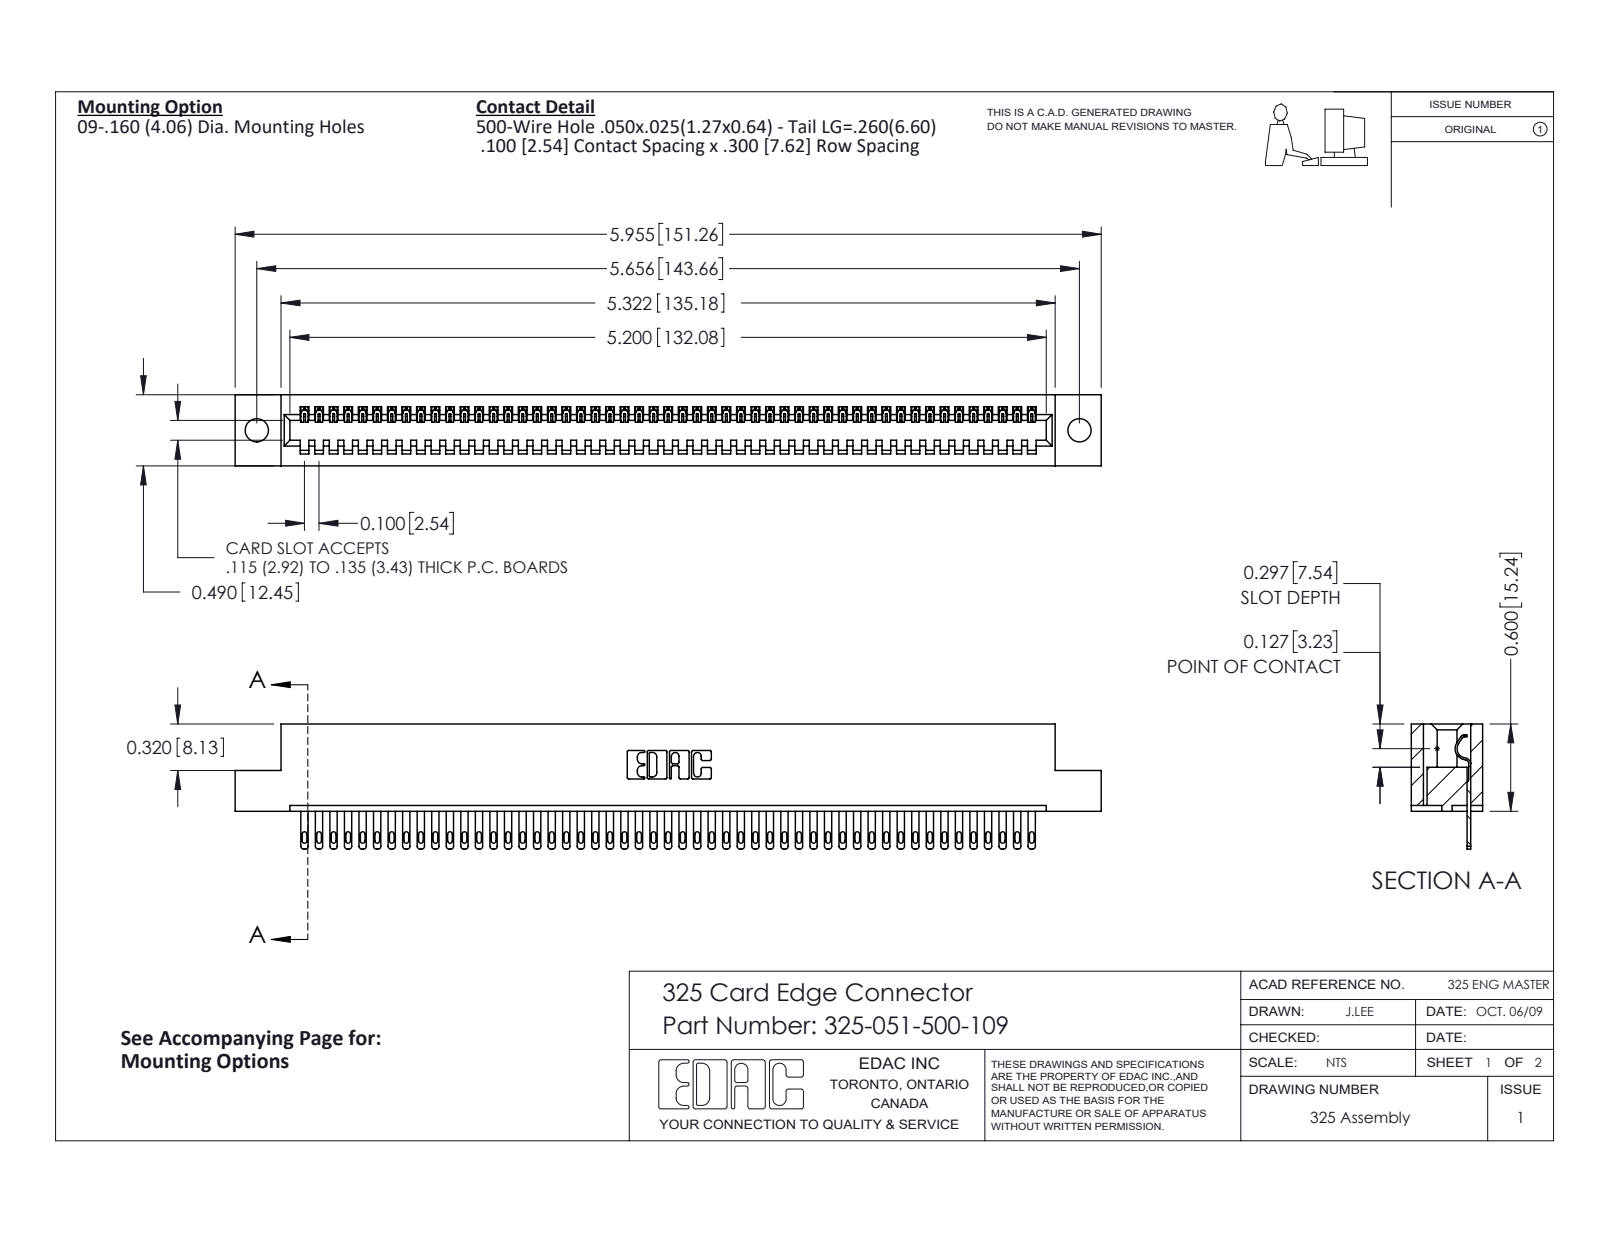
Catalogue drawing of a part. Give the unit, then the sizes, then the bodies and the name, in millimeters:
Units: millimetres
Overall size (bounding box): 151.3 × 21.8 × 12.4
Round holes (diameter × count): ⌀4.1 ×2
Partial cylindrical surfaces — rounded edges, fillets, slot ends (radius × count): R0.2 ×102, R0.4 ×102, R0.5 ×102, R0.3 ×22, R0.2 ×6, R0.8 ×6, R0.7 ×3, R0.4 ×1
Main face-to-face distances: 2.1, 10.3, 12.4, 7.6, 2.7, 9.7, 0.6, 8.3, 14.2, 6.7
Hole centre spacings: 143.7
Volume: 19 070 mm³ · Surface area: 21 010 mm²
Bodies: 52 solids, 2868 faces (1906 planar, 962 cylindrical, 0 other)
Part name (STEP PRODUCT): 325-292-001_325-293-100; 325-051-500-109; 325 Part_.160 TH
STEP written by: SolidWorks 2016 (CONFIG_CONTROL_DESIGN)
